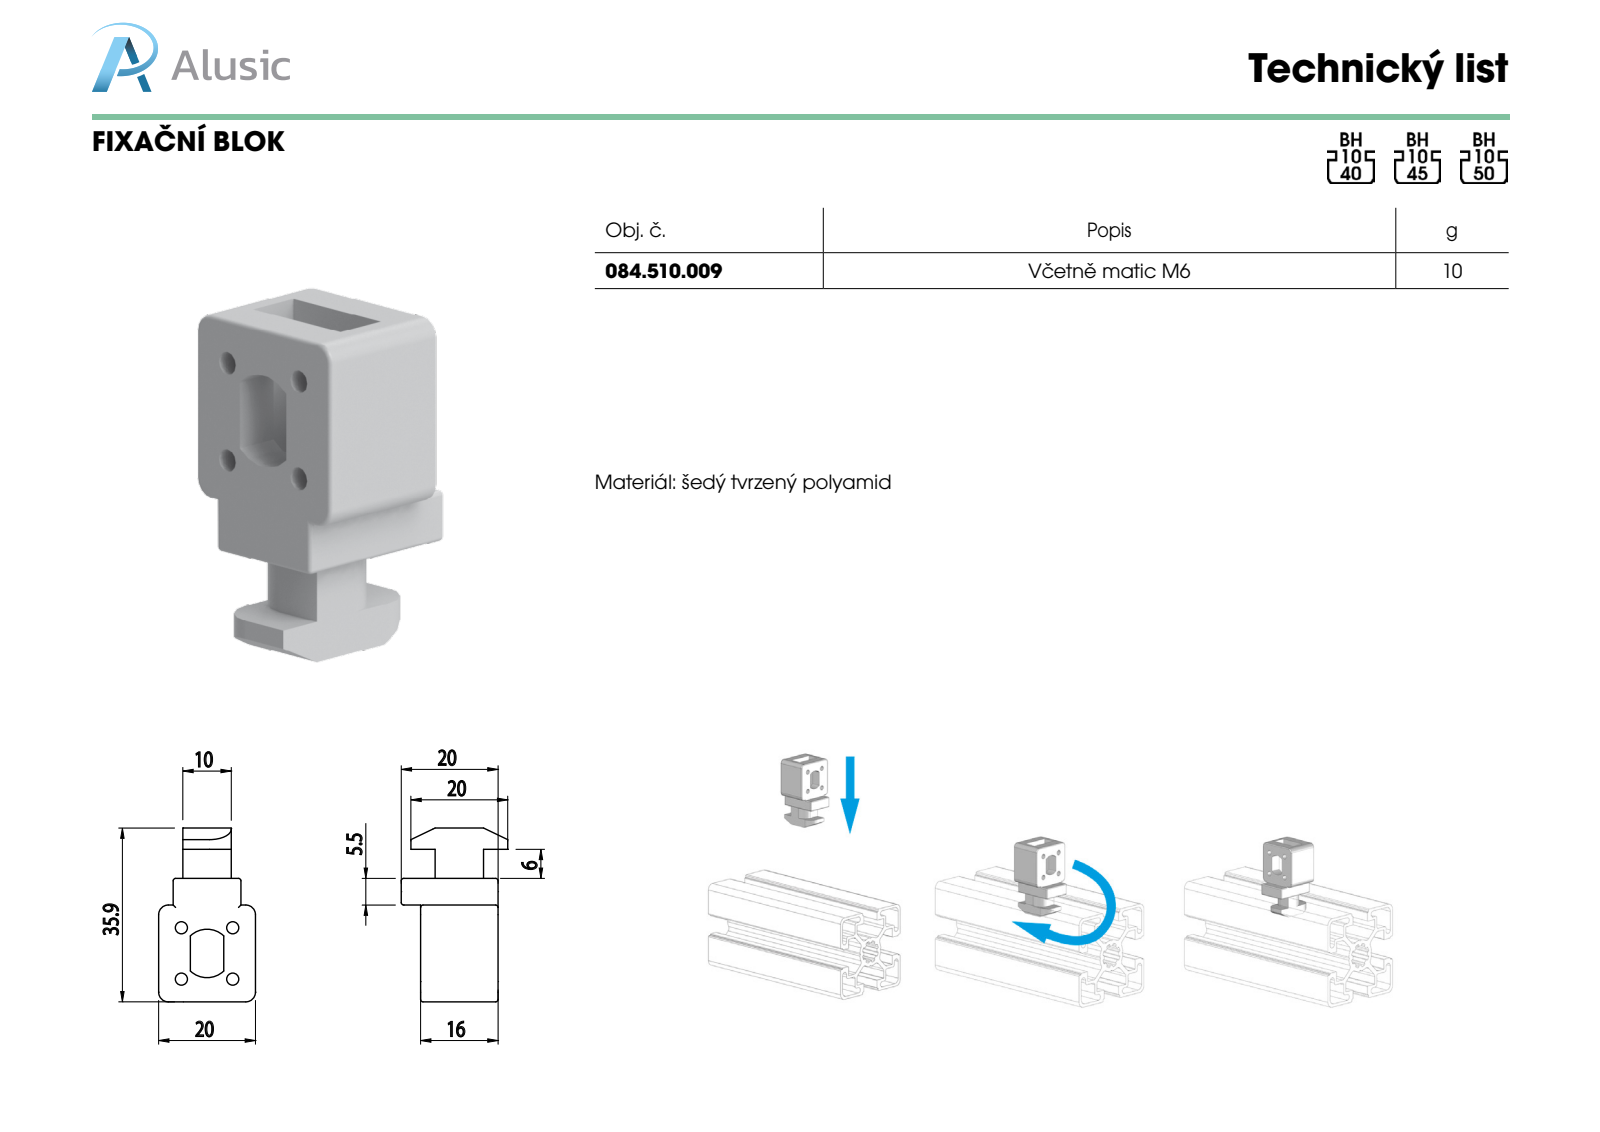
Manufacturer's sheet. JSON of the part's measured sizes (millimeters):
{"part_name": "084.510.009", "step_written_by": "SolidWorks 2012 (CONFIG_CONTROL_DESIGN)", "units": "millimeters", "bodies": {"solids": 1, "faces": 89, "planar": 42, "cylindrical": 33, "other": 14}, "overall_size": [35.9, 22, 20], "volume_mm3": 6770, "surface_area_mm2": 3835, "partial_cylinders_radius": [[0.5, 19], [2, 4], [4.5, 4], [5, 1]], "face_to_face_distances": [2, 5, 3, 20, 9, 11, 14, 12, 13.5, 16.5]}
